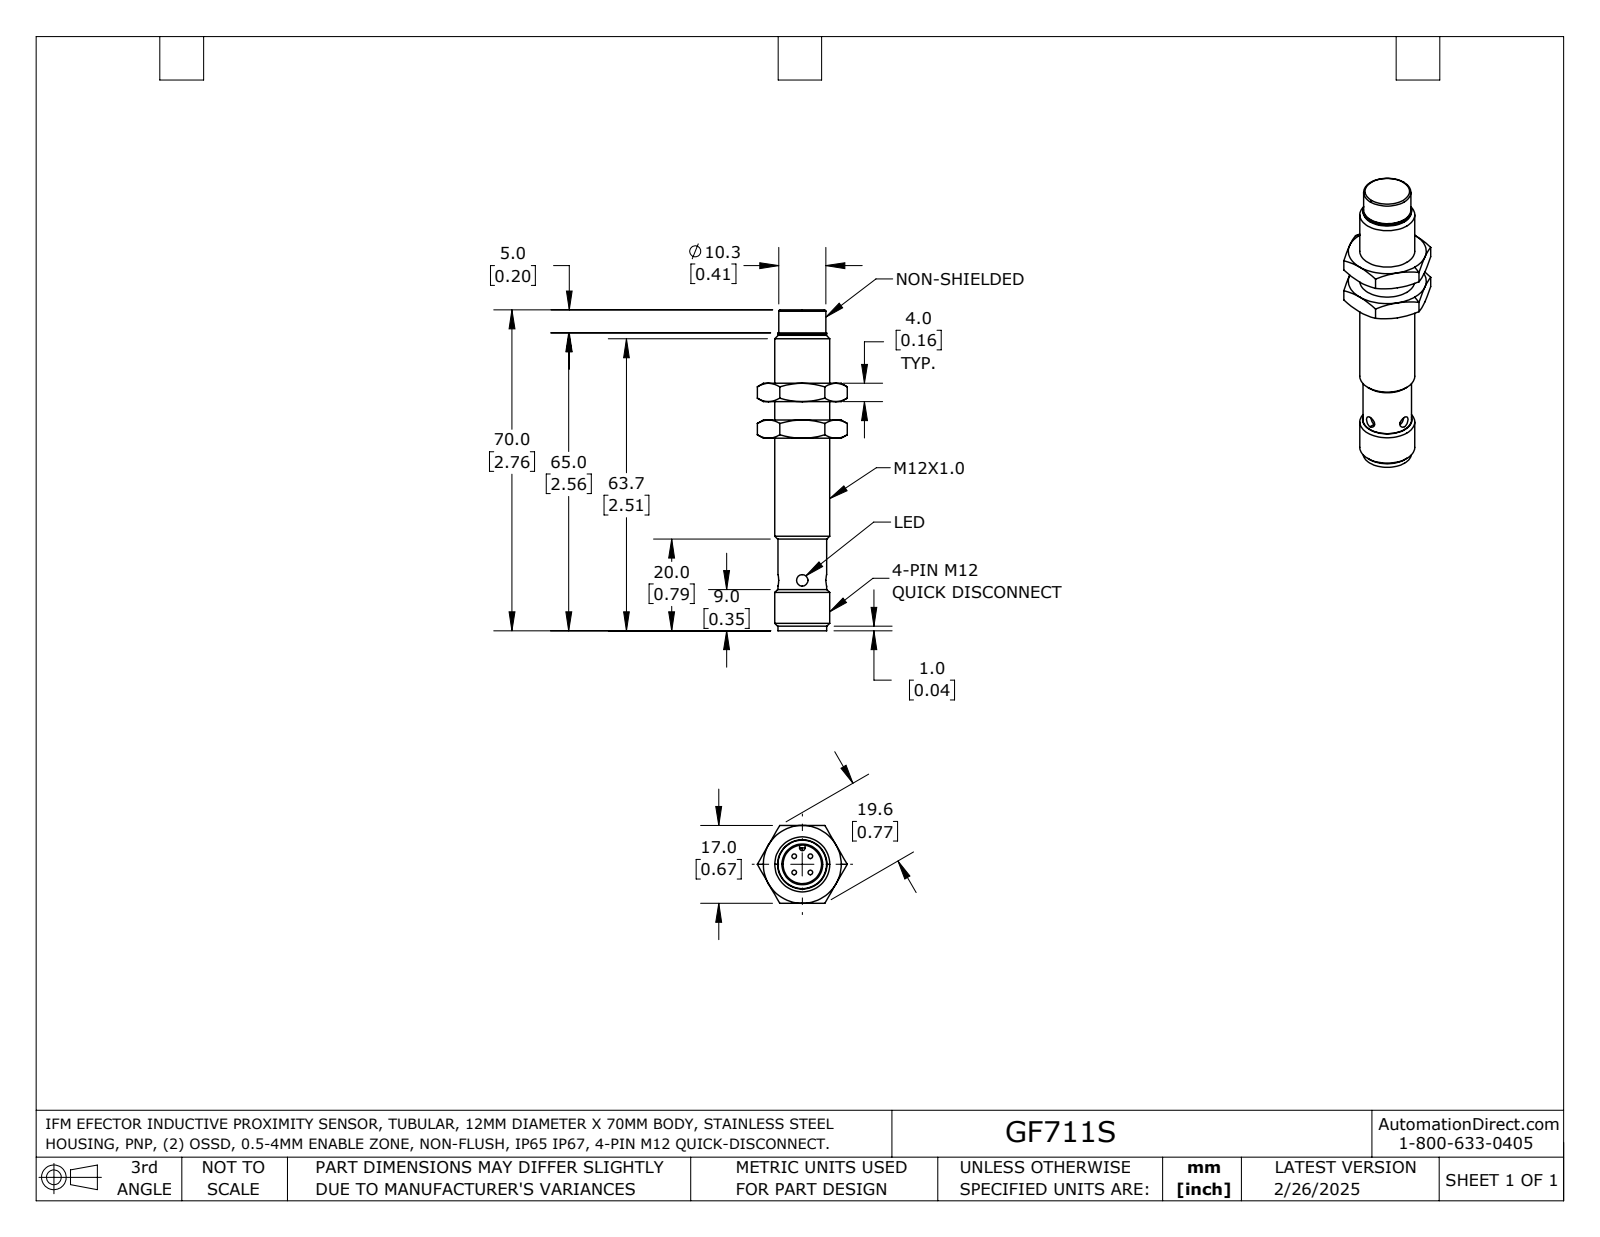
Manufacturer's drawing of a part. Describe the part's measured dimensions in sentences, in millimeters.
The part is named "GF711S". Its 3-D file was written by "SolidWorks 2024 (AUTOMOTIVE_DESIGN)". It is 3 solids with 117 faces: 26 planar, 33 cylindrical and 58 other. Overall it measures 70 by 19.63 by 17 millimeters. Its volume is 8 126 cubic millimeters and its surface area 4 343 square millimeters. Round holes: 2 of diameter 2.5, 1 of diameter 8.4, 1 of diameter 10.92. Round bosses or shafts: 1 of diameter 12, 1 of diameter 10.6, 1 of diameter 10.3. Partial cylindrical surfaces (rounded edges, fillets, slot ends): 1 of radius 0.6, 1 of radius 4. The main face-to-face distances are 4, 8, 17, 12, 20, 16, 24, 28, 61.1, 45.1.
